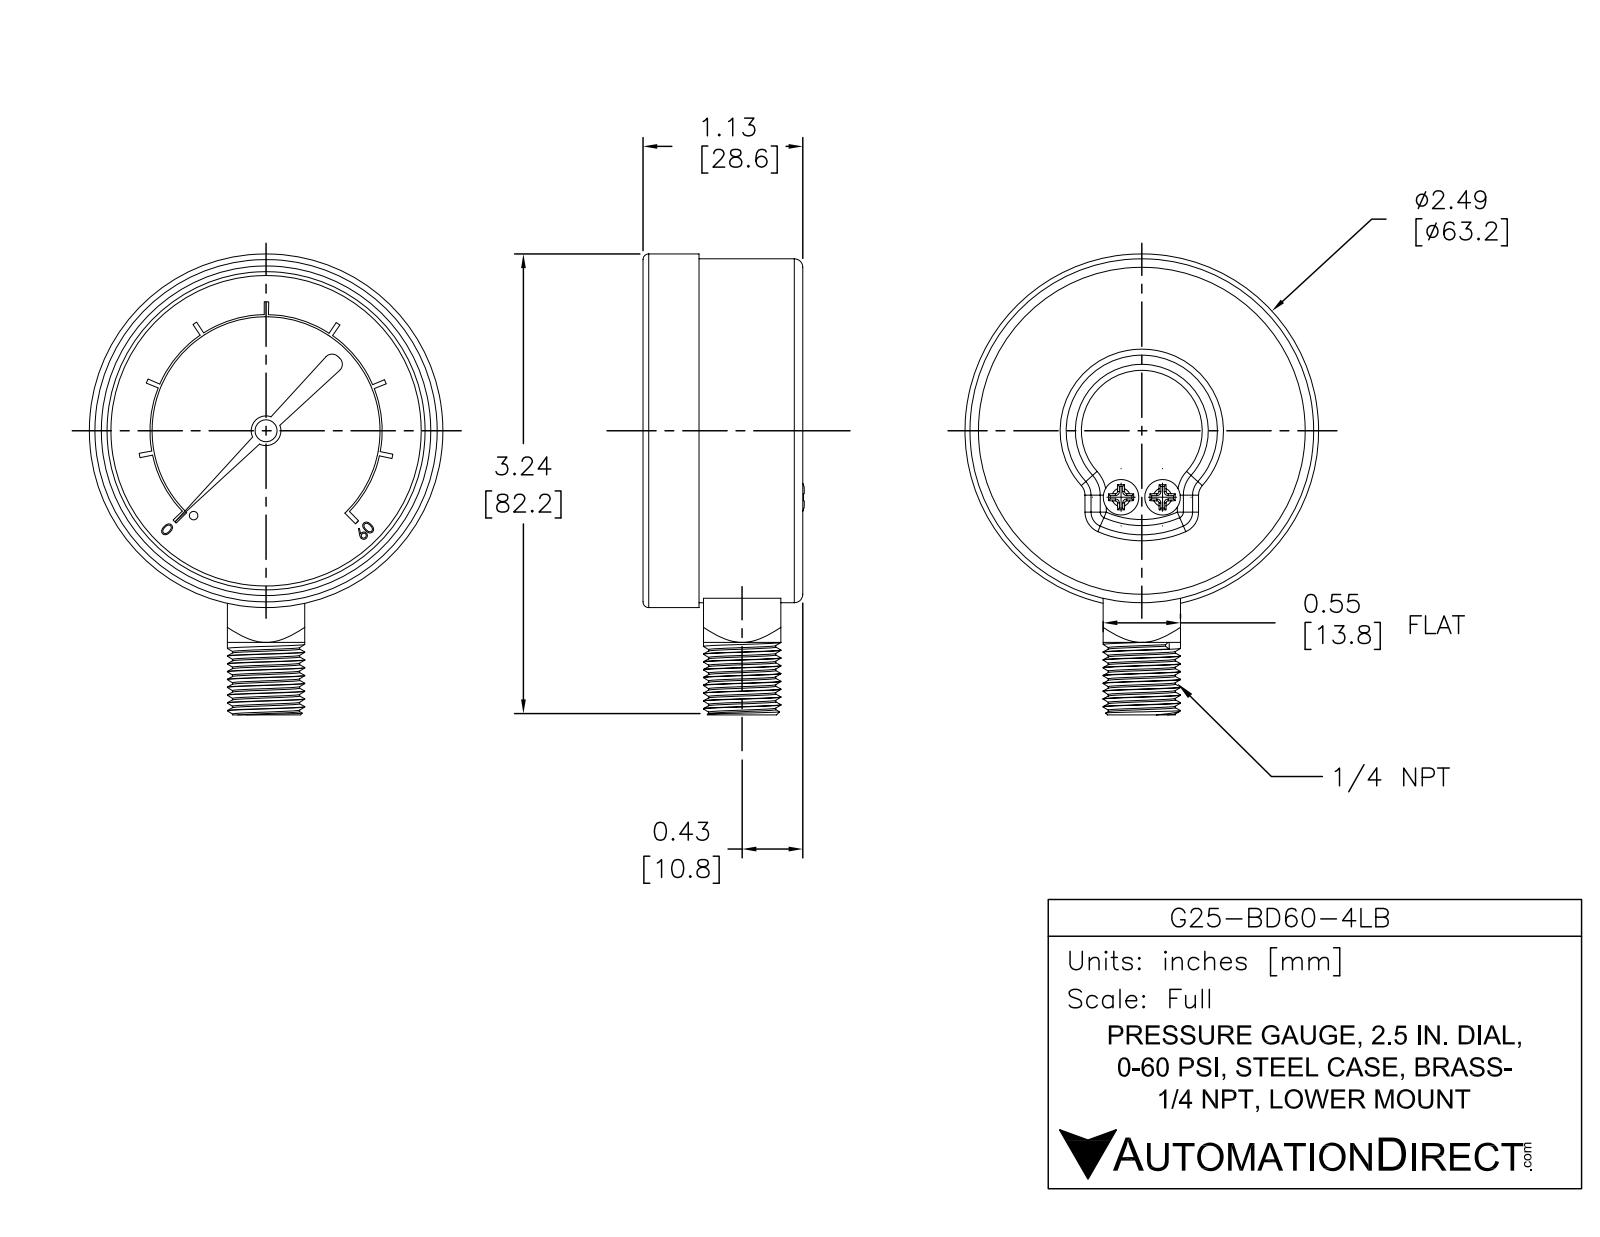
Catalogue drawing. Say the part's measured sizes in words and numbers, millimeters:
The part is named "G25-BD60-4LB". Its 3-D file was written by "SolidWorks 2021 (AUTOMOTIVE_DESIGN)". It is 1 solid with 210 faces: 111 planar, 35 cylindrical and 64 other. Overall it measures 82.4 by 63.2 by 28.8 millimeters. Its volume is 70 270 cubic millimeters and its surface area 14 450 square millimeters. Round holes: 1 of diameter 3.6, 1 of diameter 55.5. Round bosses or shafts: 2 of diameter 6.4, 1 of diameter 63.2, 1 of diameter 61.5, 1 of diameter 13.8, 1 of diameter 3.9, 1 of diameter 3.1, 1 of diameter 1.5. Partial cylindrical surfaces (rounded edges, fillets, slot ends): 6 of radius 1.5, 1 of radius 2.7, 1 of radius 20.4, 1 of radius 20.8. The main face-to-face distances are 21.2, 2.5, 18.7, 28.6, 26, 7.4, 13.8, 18.6, 16, 2.6.
